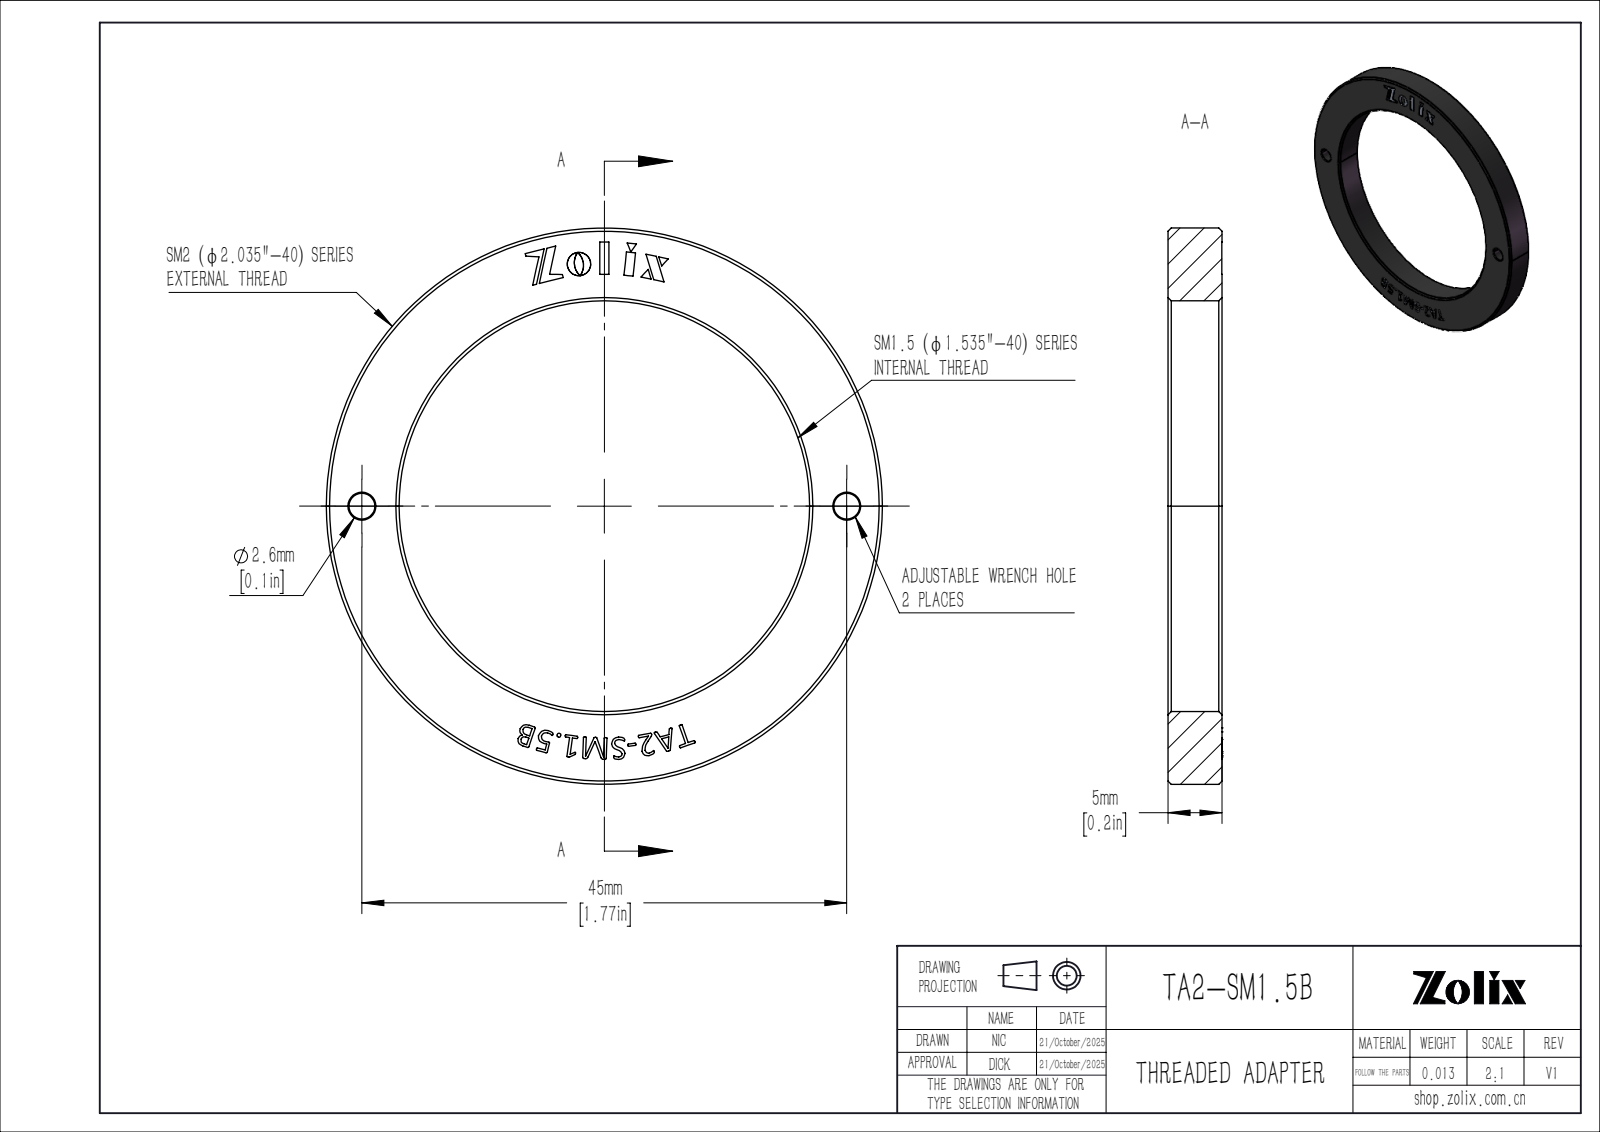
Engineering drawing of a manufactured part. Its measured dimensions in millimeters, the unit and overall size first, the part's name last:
Units: millimetres
Overall size (bounding box): 51.6 × 51.6 × 5
Round holes (diameter × count): ⌀2.4 ×2, ⌀38.1 ×1
Round bosses / shafts (diameter × count): ⌀51.6 ×1
Main face-to-face distances: 5, 4.98, 3, 0.86, 2.16, 0.84, 2.18, 1.93, 2.17, 0.83
Hole centre spacings: 22.5, 45
Volume: 4 684 mm³ · Surface area: 3 271 mm²
Bodies: 1 solid, 339 faces (223 planar, 8 cylindrical, 108 other)
Part name (STEP PRODUCT): TA2-SM1.5B
STEP written by: SolidWorks 2020 (CONFIG_CONTROL_DESIGN)
